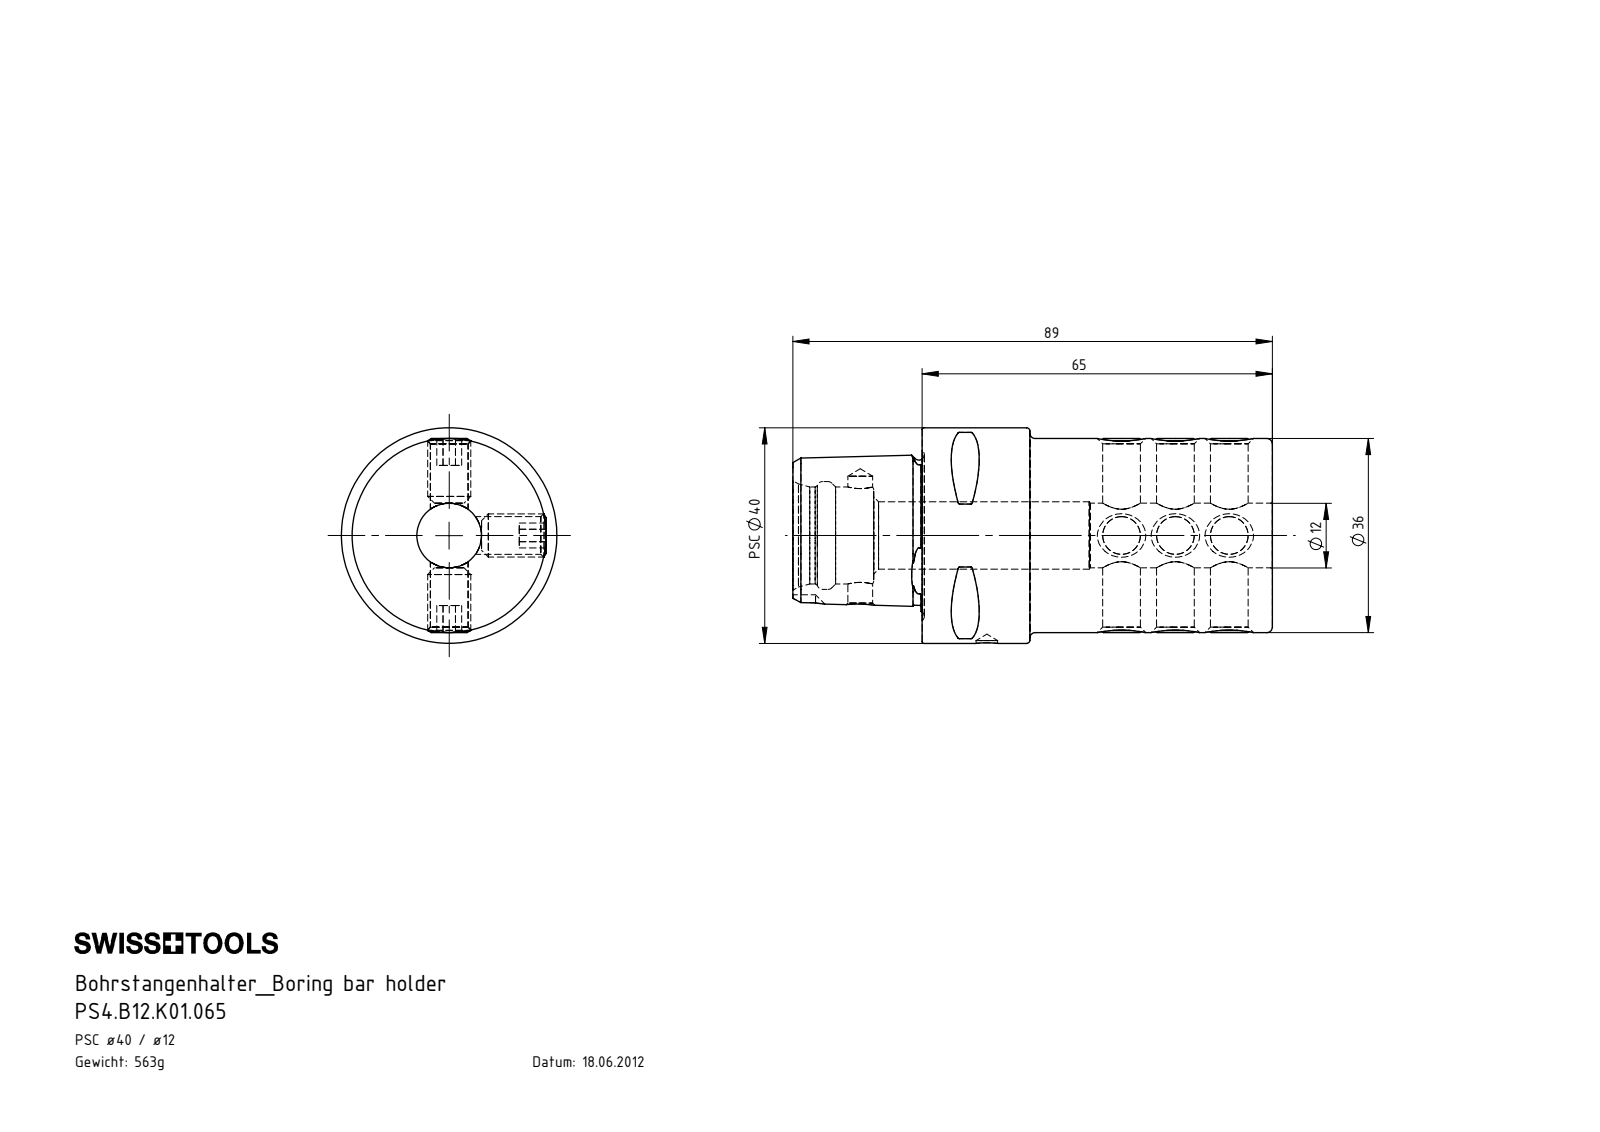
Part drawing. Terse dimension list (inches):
name: ISO 4026 - M8 x 12_PreviewCfg; PS4-B12.K01.065_A; PS4.B12.K01.065
written by: SolidWorks 2017 (AUTOMOTIVE_DESIGN)
unit: in
bodies: 10 solids, 308 faces (101 planar, 65 cylindrical, 142 other)
size: 3.504 × 1.575 × 1.575
volume: 4.378 in³; area: 32.97 in²
holes: 6× ⌀0.276, 1× ⌀0.157, 1× ⌀0.181, 1× ⌀0.472, 1× ⌀0.492, 1× ⌀0.709, 1× ⌀0.787
bosses: 6× ⌀0.315, 1× ⌀1.575, 1× ⌀1.417
rounds: 8× R0.012, 1× R0.118
face distances: 2.559, 0.197, 0.945, 0.157, 0.394, 0.472, 0.354, 0.236, 3.504, 0.787
hole spacings: 0.394, 0.787, 0.925, 0.984, 1.378, 1.772, 1.909, 2.303
